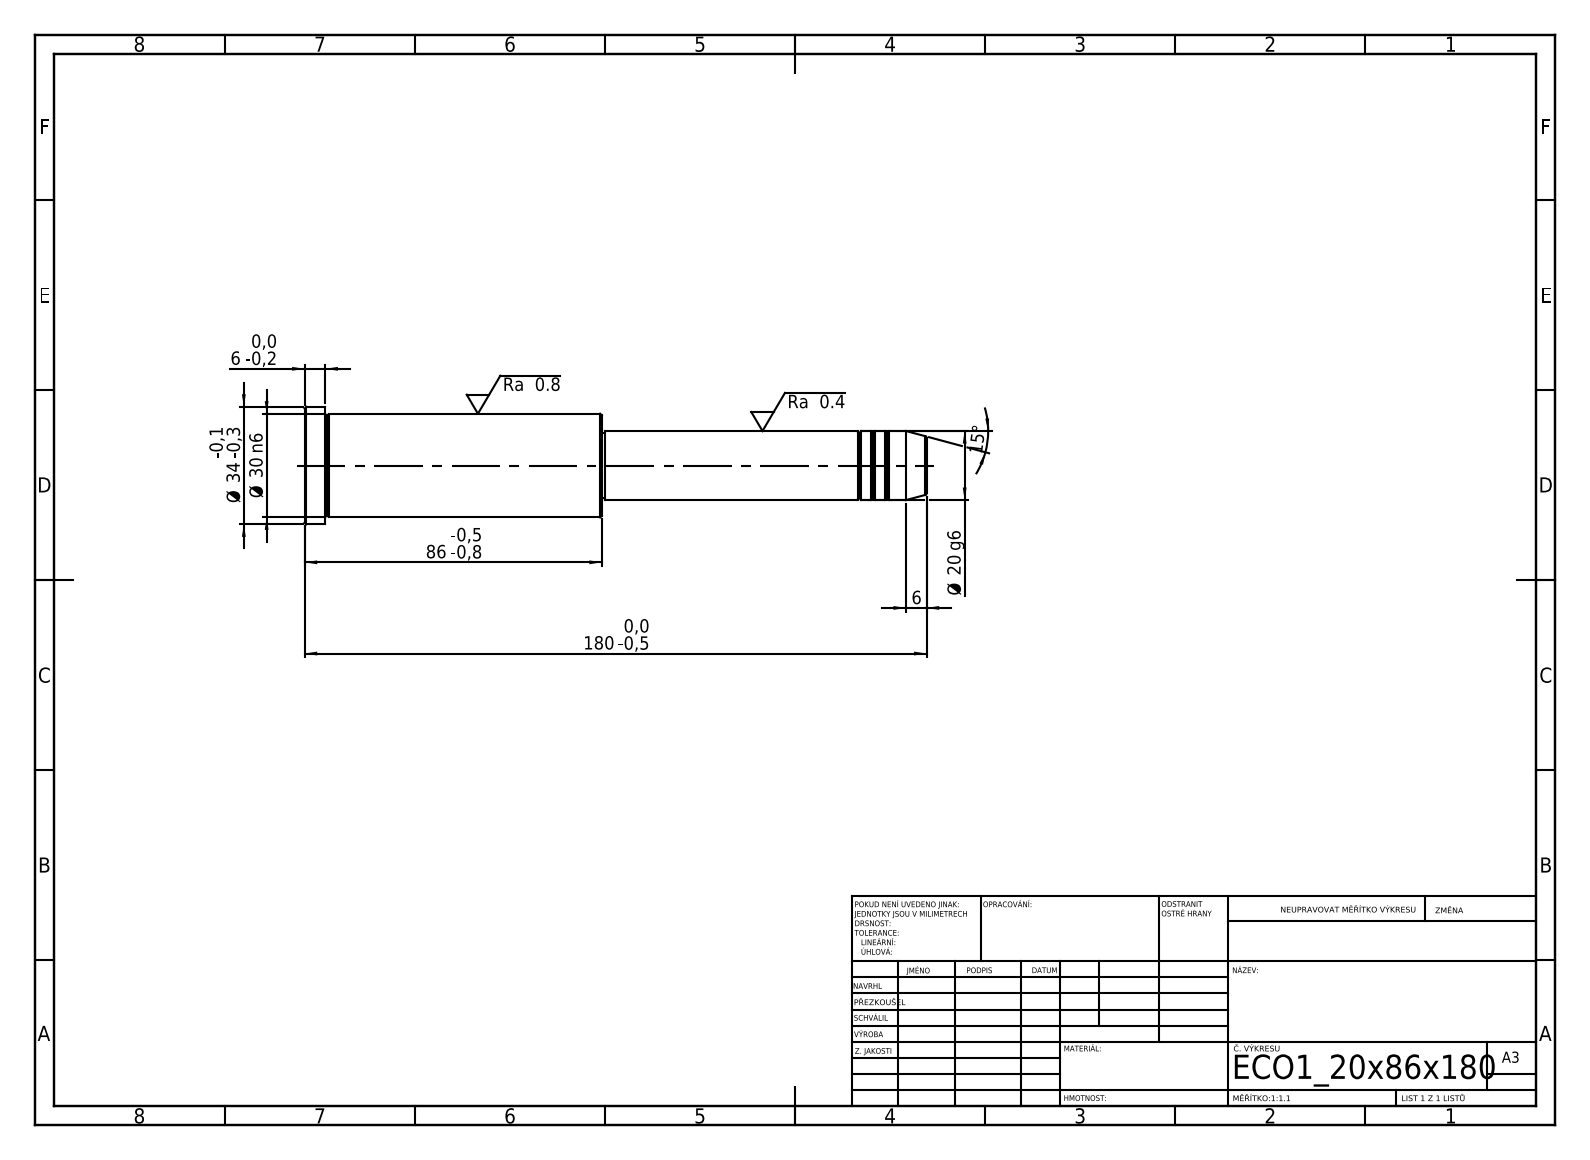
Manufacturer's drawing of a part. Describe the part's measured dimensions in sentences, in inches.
Its 3-D file was written by "SolidWorks 2019 (CONFIG_CONTROL_DESIGN)". It is 1 solid with 43 faces: 5 planar, 14 cylindrical and 24 other. Overall it measures 7.087 by 1.339 by 1.339 inches. Its volume is 5.558 cubic inches and its surface area 24.7 square inches. Round bosses or shafts: 1 of diameter 1.339, 1 of diameter 1.181, 1 of diameter 0.787, 1 of diameter 0.748. The main face-to-face distances are 3.386, 3.701, 7.087, 6.85, 3.15, 0.236, 3.661, 0.039, 3.189, 3.425.
